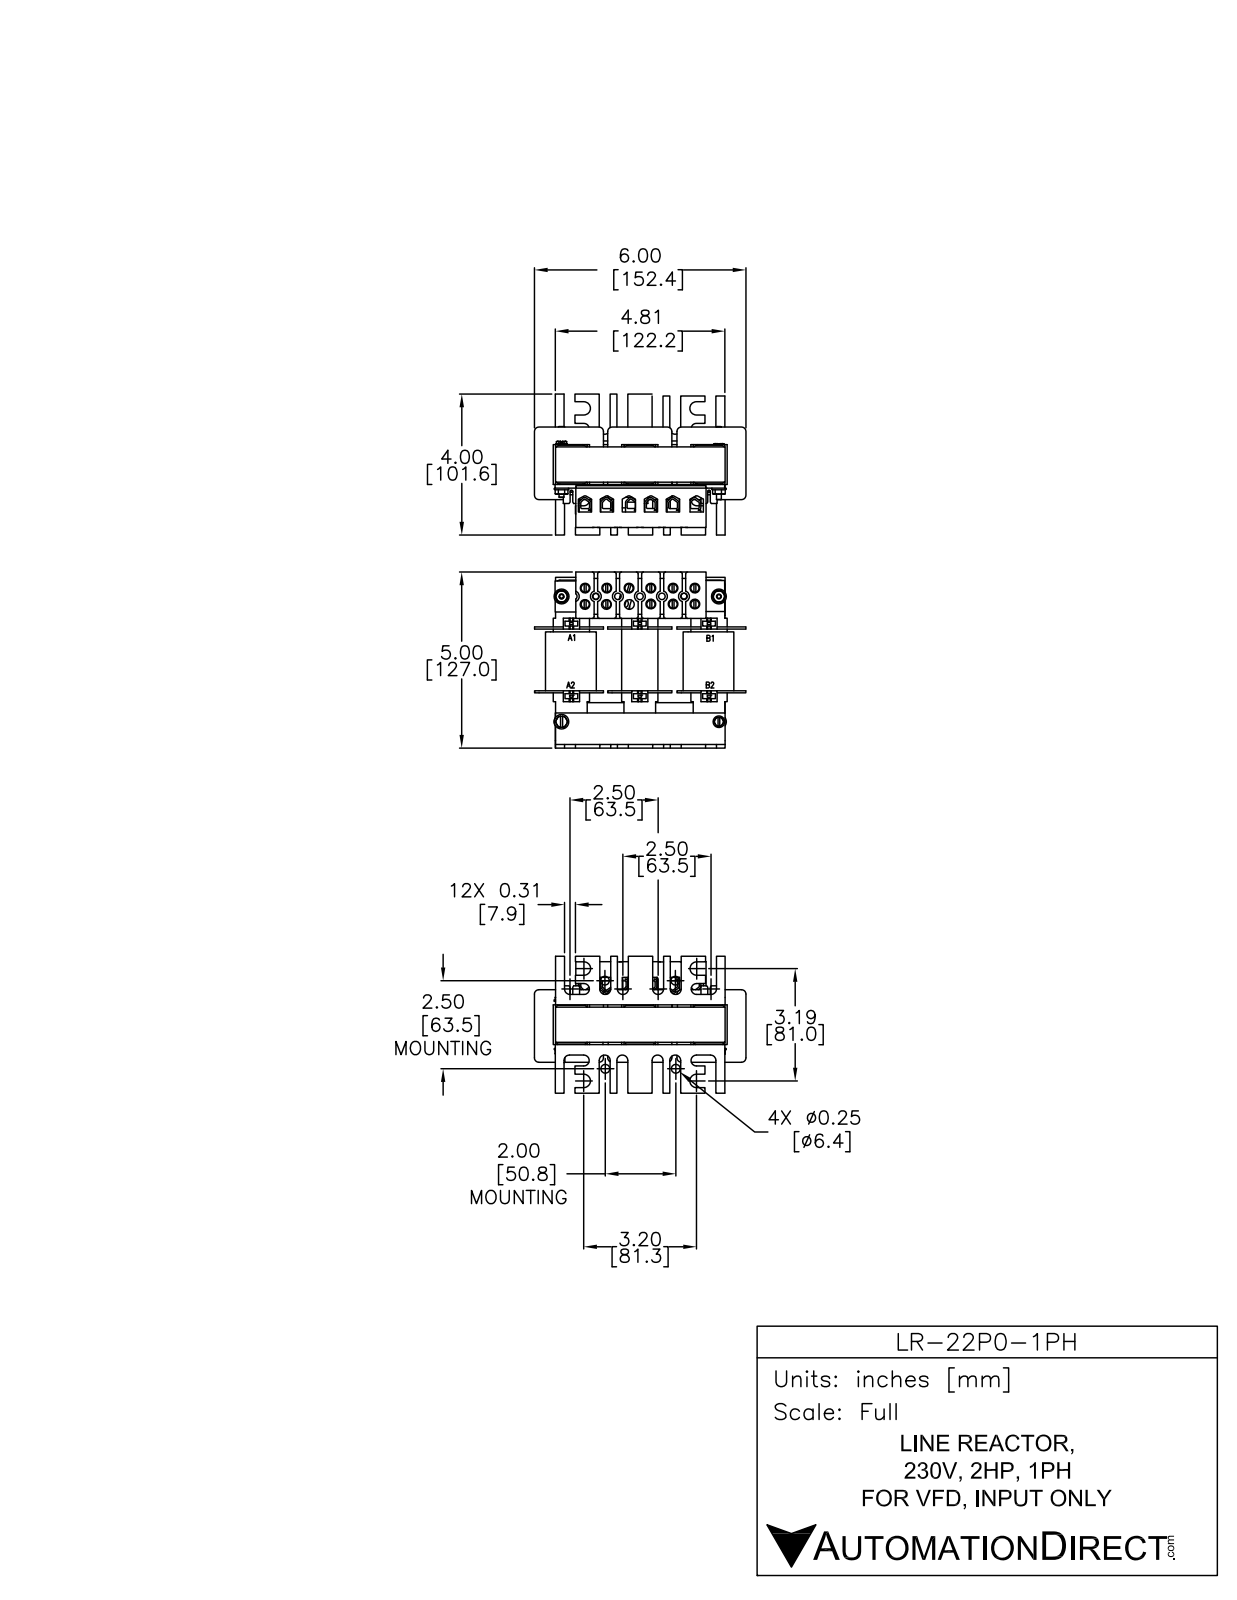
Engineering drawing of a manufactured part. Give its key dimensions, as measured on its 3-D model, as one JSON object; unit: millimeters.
{"part_name": "LR-22P0-1PH", "step_written_by": "SolidWorks 2011 (AUTOMOTIVE_DESIGN)", "units": "millimeters", "bodies": {"solids": 43, "faces": 1048, "planar": 794, "cylindrical": 222, "other": 32}, "overall_size": [144.75, 131.2, 98.38], "volume_mm3": 540879, "surface_area_mm2": 167068, "round_holes": [[7, 12], [7.75, 5]], "round_bosses_or_shafts": [[7, 12], [10.25, 4], [8, 4], [7.75, 2], [7.5, 2], [3.4, 2], [3.25, 2]], "partial_cylinders_radius": [[3.94, 16], [1.82, 12], [2.68, 12], [2.71, 12], [5, 12], [6, 12], [4.83, 4], [0.86, 3]], "face_to_face_distances": [2.5, 27.26, 1.5, 31.25, 5.62, 34.88, 28.76, 34.38, 7.12, 32.88], "hole_center_spacings": [16, 32, 21.26, 34.93, 48, 14, 50, 10.34]}
